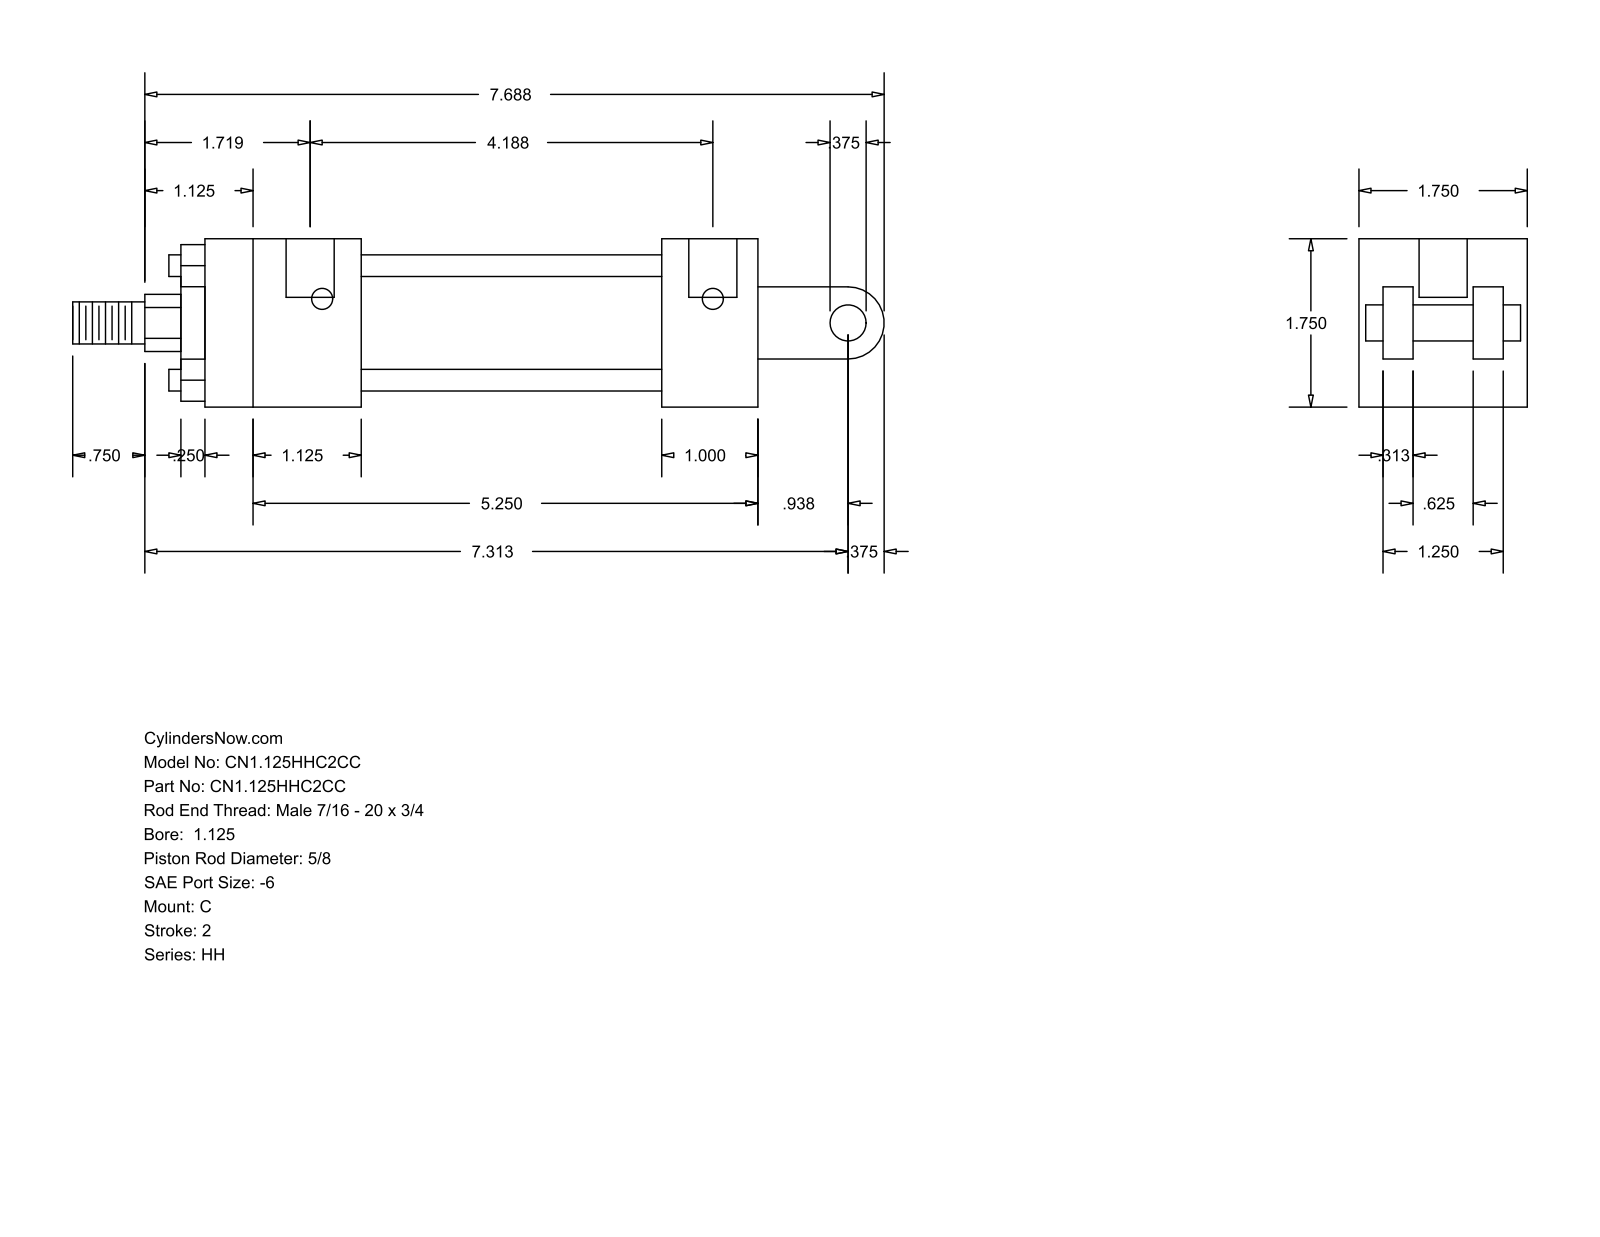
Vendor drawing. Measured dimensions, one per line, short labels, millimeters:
name: HH_C__0112_0.625
written by: GSSL Pune (CONFIG_CONTROL_DESIGN)
unit: mm
bodies: 0 solids, 99 faces (70 planar, 29 cylindrical, 0 other)
size: 214.31 × 44.45 × 44.45
holes: 4× ⌀5.56, 2× ⌀12.7
bosses: 4× ⌀5.71, 1× ⌀34.92, 1× ⌀28.57, 1× ⌀15.88, 1× ⌀11.11, 1× ⌀9.53
rounds: 1× R7.54, 1× R9.53
face distances: 44.46, 6.35, 31.76, 14.29, 25.4, 30.17, 38.11, 7.94, 23.82, 12.7
hole spacings: 103.19, 3.17, 106.36
